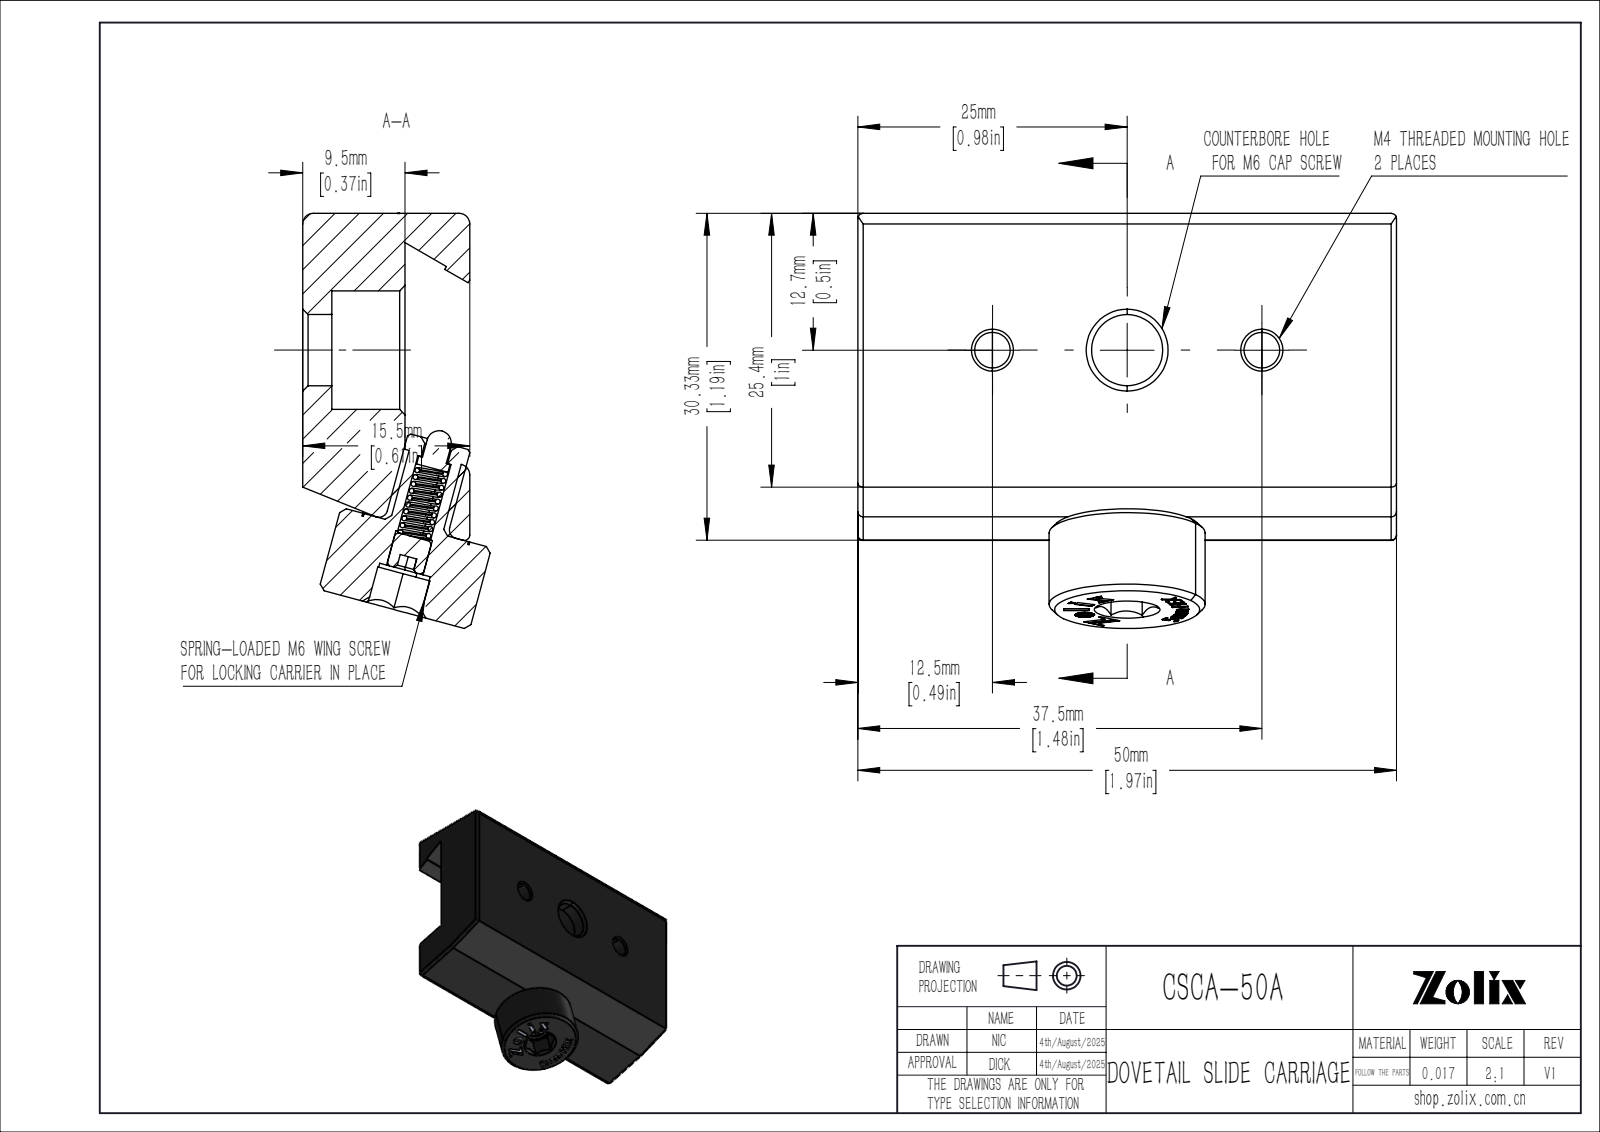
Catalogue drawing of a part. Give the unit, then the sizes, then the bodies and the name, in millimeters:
Units: millimetres
Overall size (bounding box): 50 × 38.52 × 17.4
Round holes (diameter × count): ⌀3.3 ×2, ⌀2.15 ×1, ⌀2.54 ×1, ⌀3.18 ×1, ⌀3.51 ×1, ⌀4.85 ×1, ⌀5 ×1, ⌀6.6 ×1, ⌀10.29 ×1, ⌀11 ×1
Round bosses / shafts (diameter × count): ⌀14.48 ×1, ⌀10.03 ×1, ⌀6 ×1, ⌀3.48 ×1, ⌀3 ×1, ⌀2.29 ×1
Partial cylindrical surfaces — rounded edges, fillets, slot ends (radius × count): R0.5 ×11, R1 ×3
Main face-to-face distances: 9.5, 15.5, 6, 50, 7.88, 2.7, 6.8, 12.8, 5, 3.81
Hole centre spacings: 12.5, 25
Volume: 16 772 mm³ · Surface area: 7 344 mm²
Bodies: 5 solids, 722 faces (481 planar, 68 cylindrical, 173 other)
Part name (STEP PRODUCT): CSCA-50A
STEP written by: SolidWorks 2020 (CONFIG_CONTROL_DESIGN)
